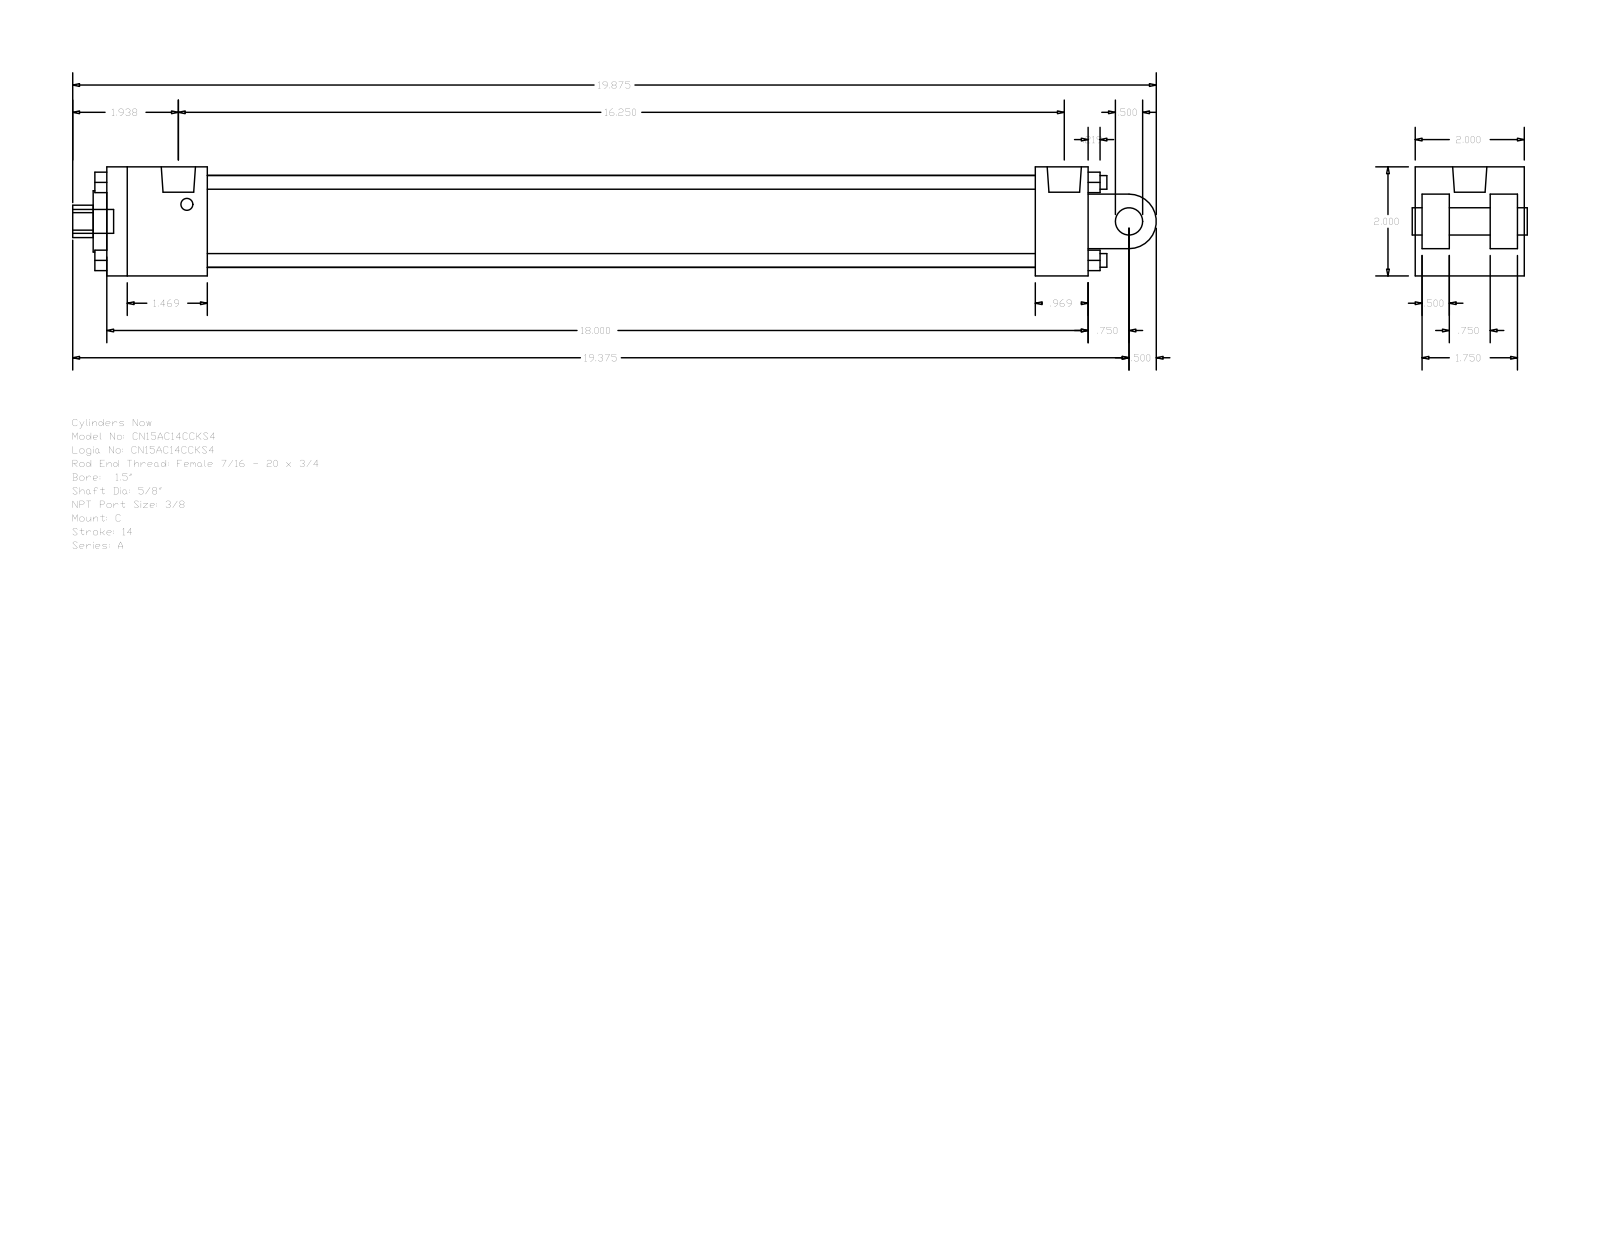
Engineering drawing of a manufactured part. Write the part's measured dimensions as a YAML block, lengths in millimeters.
part_name: "A_C__0150_0.625"
step_written_by: "GSSL Pune (CONFIG_CONTROL_DESIGN)"
units: millimeters
bodies: {solids: 0, faces: 135, planar: 102, cylindrical: 33, other: 0}
overall_size: [504.82, 50.8, 50.8]
round_holes:
  - {diameter: 5.56, count: 2}
  - {diameter: 15.88, count: 1}
  - {diameter: 15.93, count: 1}
  - {diameter: 28.57, count: 1}
  - {diameter: 42.93, count: 1}
round_bosses_or_shafts:
  - {diameter: 6.35, count: 4}
  - {diameter: 5.56, count: 2}
  - {diameter: 15.93, count: 1}
  - {diameter: 12.7, count: 1}
  - {diameter: 11.11, count: 1}
partial_cylinders:
  - {radius: 7.54, count: 1}
  - {radius: 12.7, count: 1}
face_to_face_distances: [50.8, 12.7, 457.19, 3.17, 15.87, 34.93, 47.63, 31.76, 432.59, 24.6]
hole_center_spacings: [3.97]
